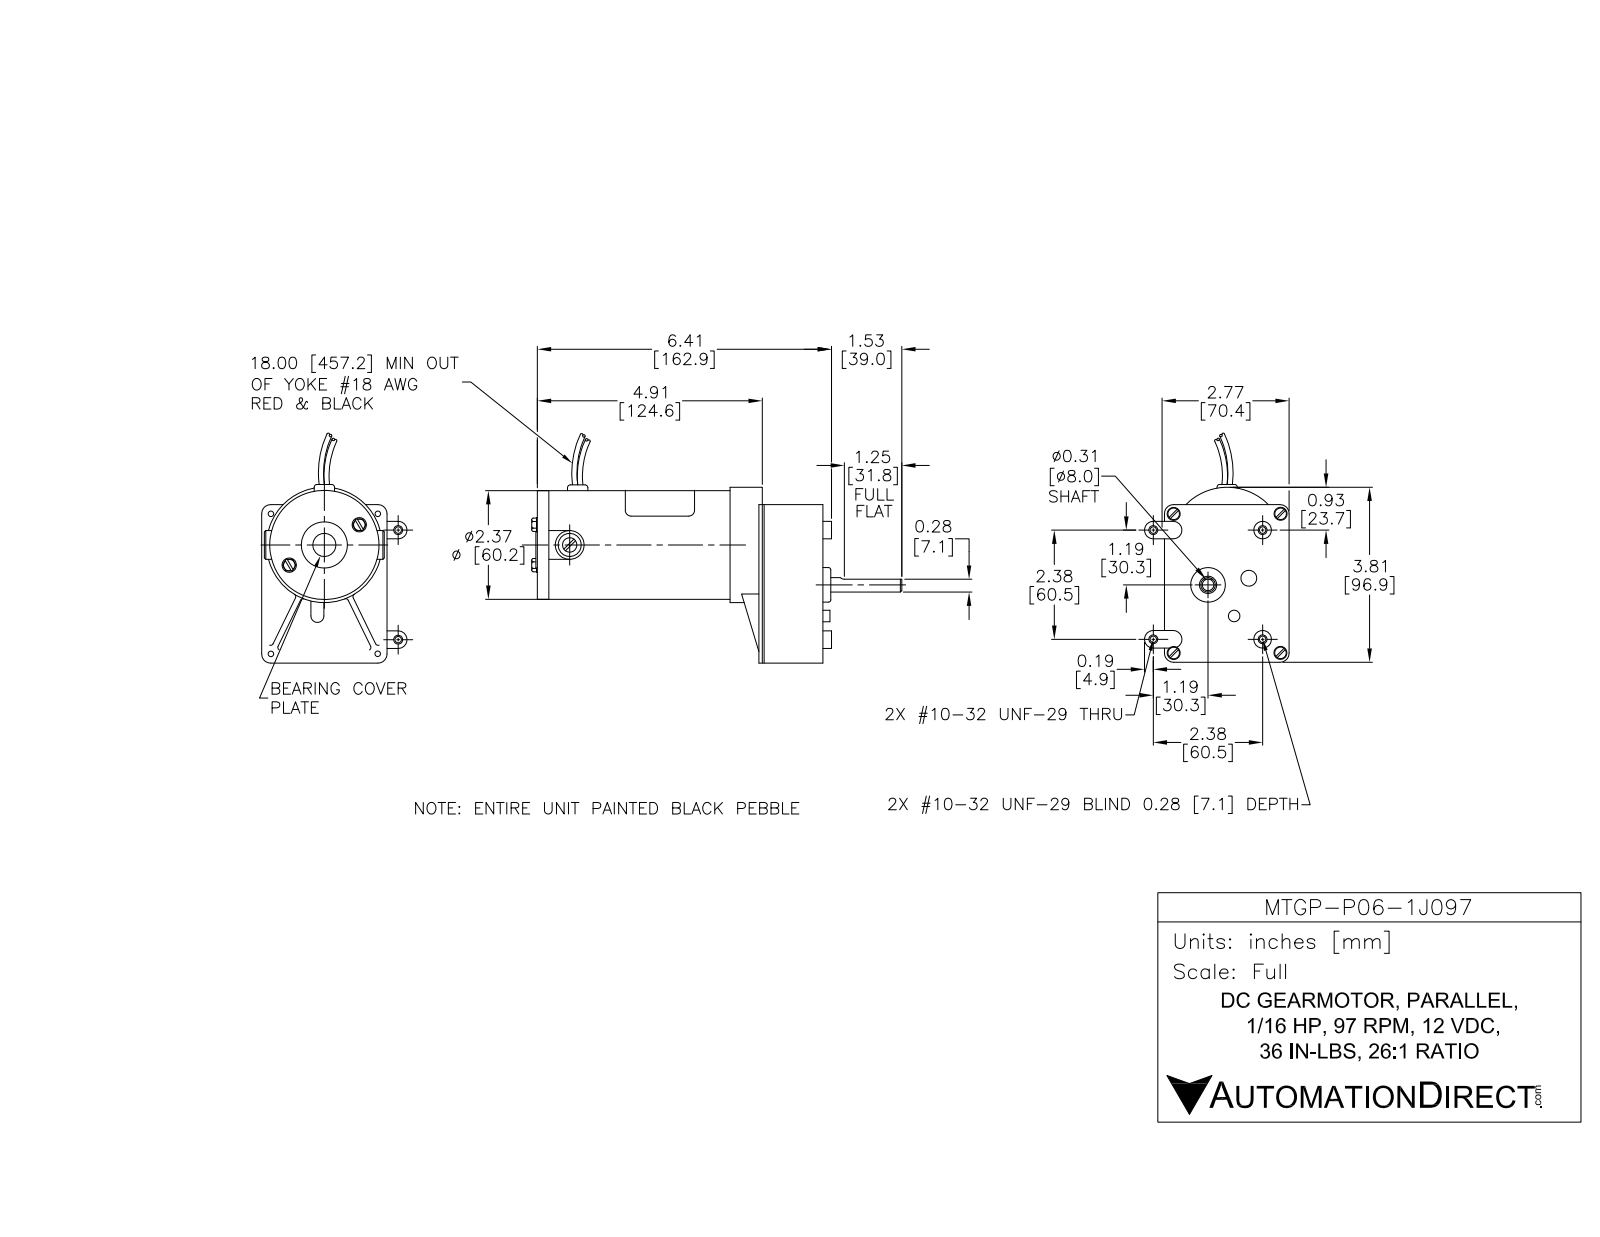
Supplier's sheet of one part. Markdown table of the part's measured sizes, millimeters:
| quantity | value |
| --- | --- |
| part name | MTGP-P06-1J097 |
| STEP written by | SolidWorks 2016 (AUTOMOTIVE_DESIGN) |
| units | millimeters |
| bodies | 27 solids, 266 faces (115 planar, 130 cylindrical, 21 other) |
| overall size | 201.2 × 129.3 × 80.8 |
| volume | 330 700 mm³ |
| surface area | 100 900 mm² |
| round holes (diameter × count) | 4.9 × 5, 1.6 × 4, 7.2 × 4, 4 × 2, 6.4 × 1, 7.9 × 1, 14.3 × 1, 25.4 × 1, 57.2 × 1 |
| round bosses / shafts (diameter × count) | 7.9 × 4, 9.7 × 2, 2.5 × 2, 62.5 × 1, 60.3 × 1, 19.1 × 1, 15.9 × 1, 15.9 × 1 |
| partial cylindrical surfaces (radius × count) | 0.8 × 10, 2.5 × 4, 4.8 × 4, 6.4 × 2, 3.4 × 1, 3.6 × 1, 31 × 1 |
| main face-to-face distances | 35.6, 6.4, 122.8, 158.3, 116.4, 152, 106.5, 100.2, 16.2, 51.8 |
| hole center spacings | 31.1, 43.9, 9.5, 11.2, 22.2, 33.2, 33.8, 39.1 |
